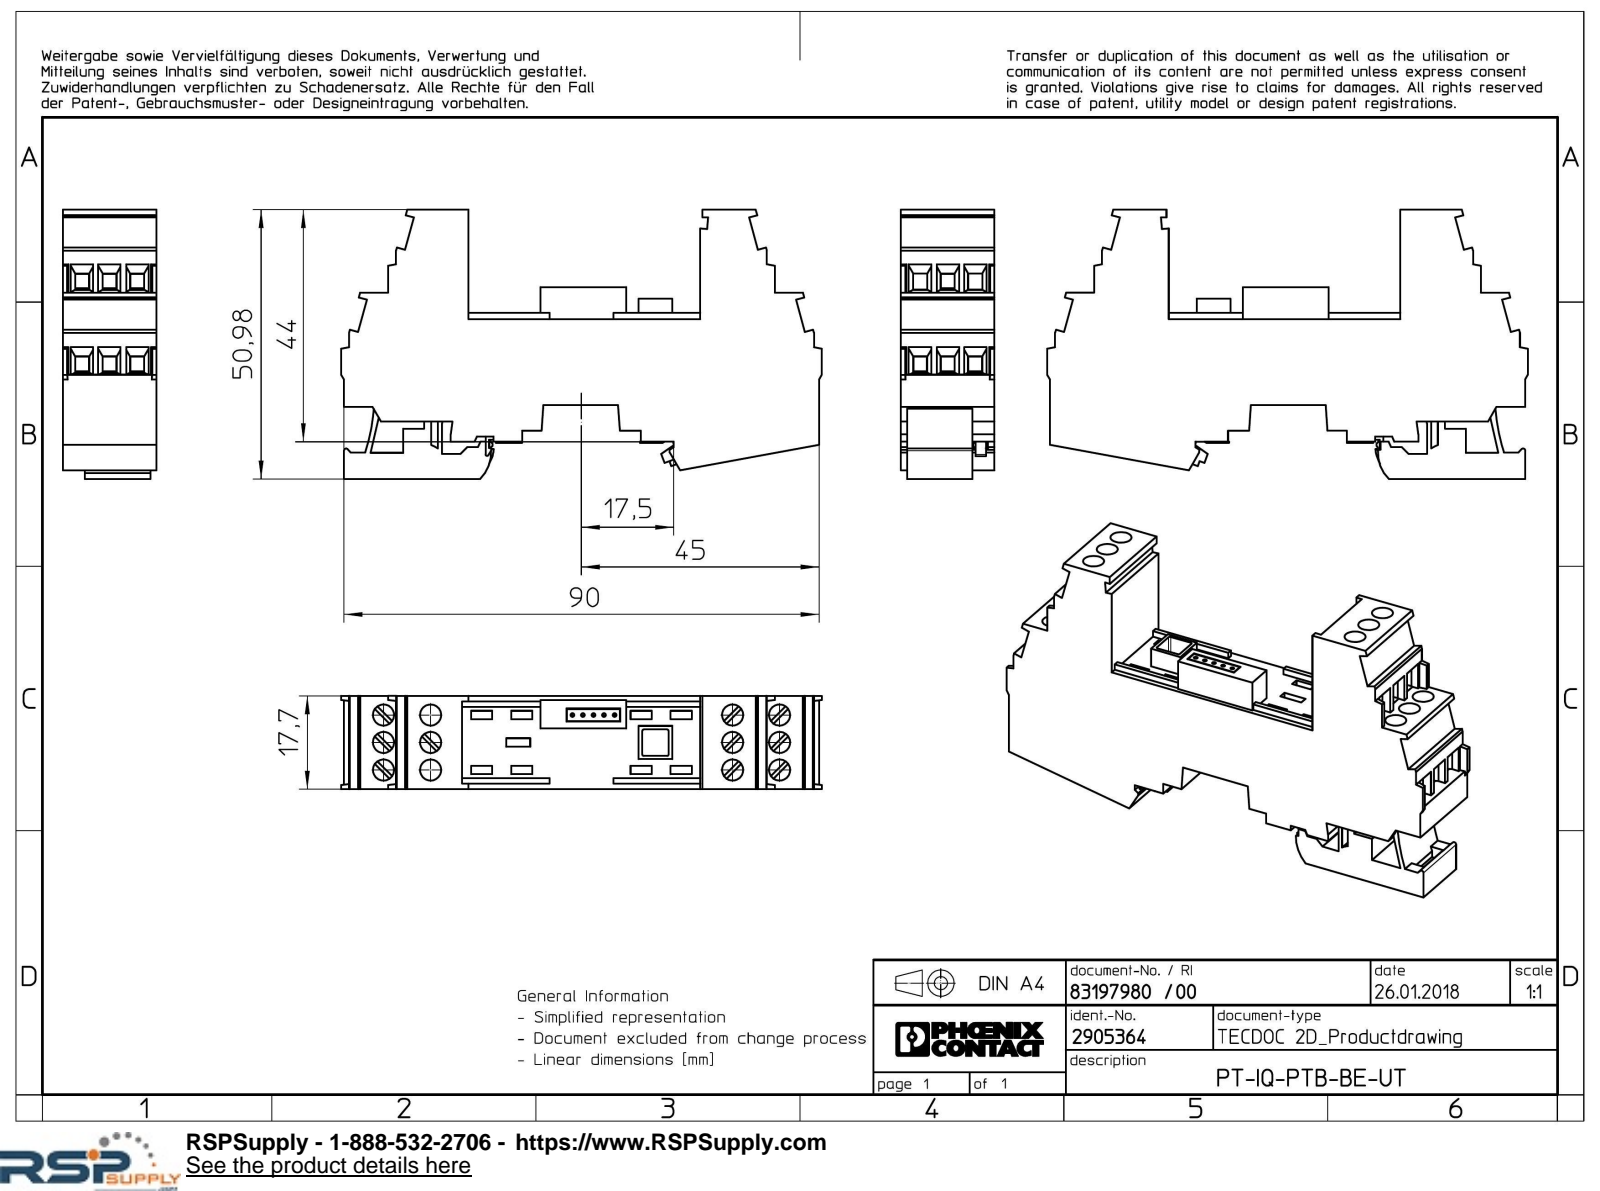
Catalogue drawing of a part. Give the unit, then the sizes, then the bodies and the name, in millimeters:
Units: millimetres
Overall size (bounding box): 91.05 × 50.98 × 17.7
Round holes (diameter × count): ⌀4 ×12, ⌀0.7 ×5
Partial cylindrical surfaces — rounded edges, fillets, slot ends (radius × count): R0.3 ×5, R0.4 ×1, R4 ×1, R9.5 ×1, R36.42 ×1
Main face-to-face distances: 17.7, 2.1, 3.1, 15.7, 30.28, 3.8, 16.33, 45.1, 50.98, 20.7
Hole centre spacings: 5.2, 10.31, 66.3, 8.9, 66.1, 2, 10.4, 13.69
Volume: 44 743 mm³ · Surface area: 15 777 mm²
Bodies: 1 solid, 633 faces (587 planar, 45 cylindrical, 1 other)
Part name (STEP PRODUCT): PT_IQ_PTB_BE_UT-select
STEP written by: Creo Elements/Direct Modeling 20.1A 29-Sep-2018 (C) Parametric Technology GmbH (AUTOMOTIVE_DESIGN)
